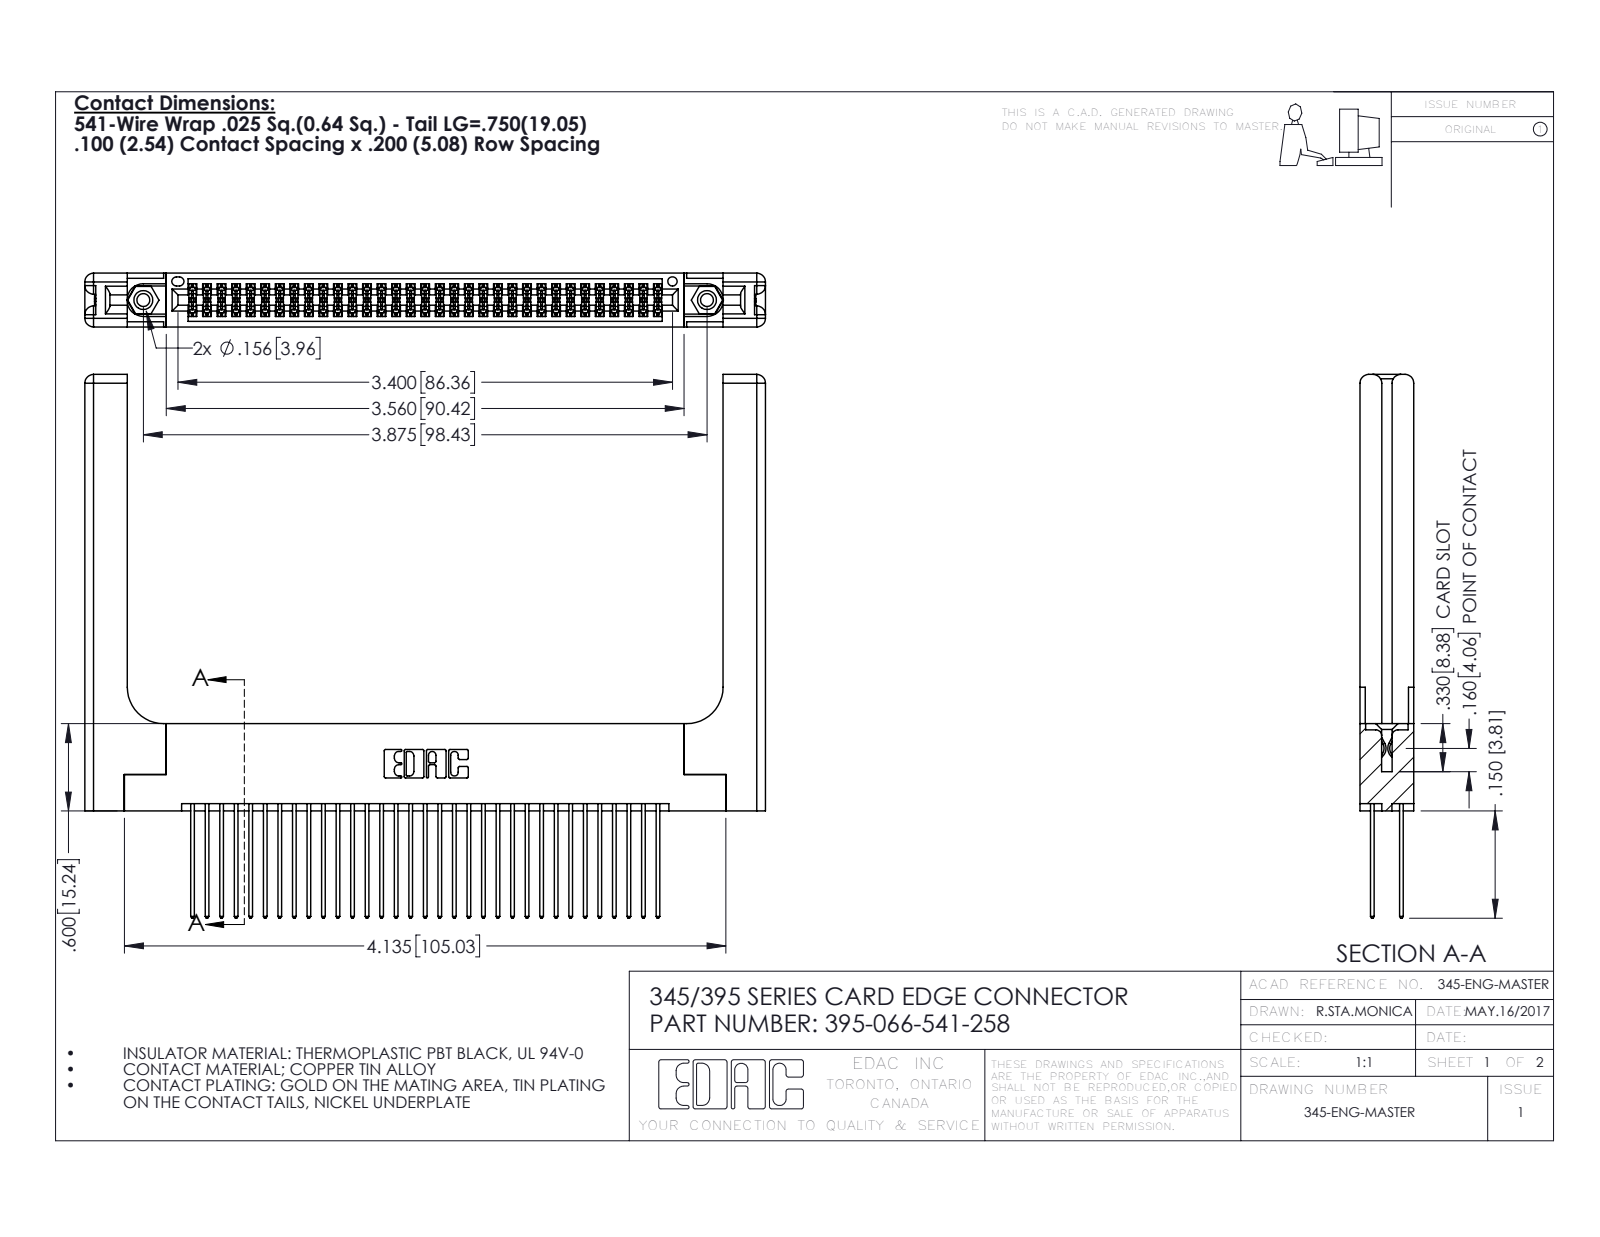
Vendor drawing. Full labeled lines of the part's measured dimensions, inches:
Part name (STEP PRODUCT): 345-292-001_345-293-141; 345-220-058_345-220-058; 395-066-541-258; 345-250-001_345-250-001-102 (+1 more)
STEP written by: SolidWorks 2016 (CONFIG_CONTROL_DESIGN)
Units: inches
Bodies: 71 solids, 3682 faces (2406 planar, 1216 cylindrical, 60 other)
Overall size (bounding box): 4.679 × 3.737 × 0.37
Volume: 1.24 in³ · Surface area: 37.46 in²
Round holes (diameter × count): ⌀0.089 ×2, ⌀0.125 ×2, ⌀0.156 ×2, ⌀0.064 ×1
Round bosses / shafts (diameter × count): ⌀0.155 ×2
Partial cylindrical surfaces — rounded edges, fillets, slot ends (radius × count): R0.006 ×99, R0.01 ×66, R0.01 ×22, R0.06 ×16, R0.007 ×6, R0.031 ×6, R0.026 ×3, R0.014 ×2
Main face-to-face distances: 0.072, 0.298, 0.37, 0.2, 0.098, 0.272, 0.025, 0.225, 0.175, 0.148
Hole centre spacings: 0.27, 3.64, 3.875
